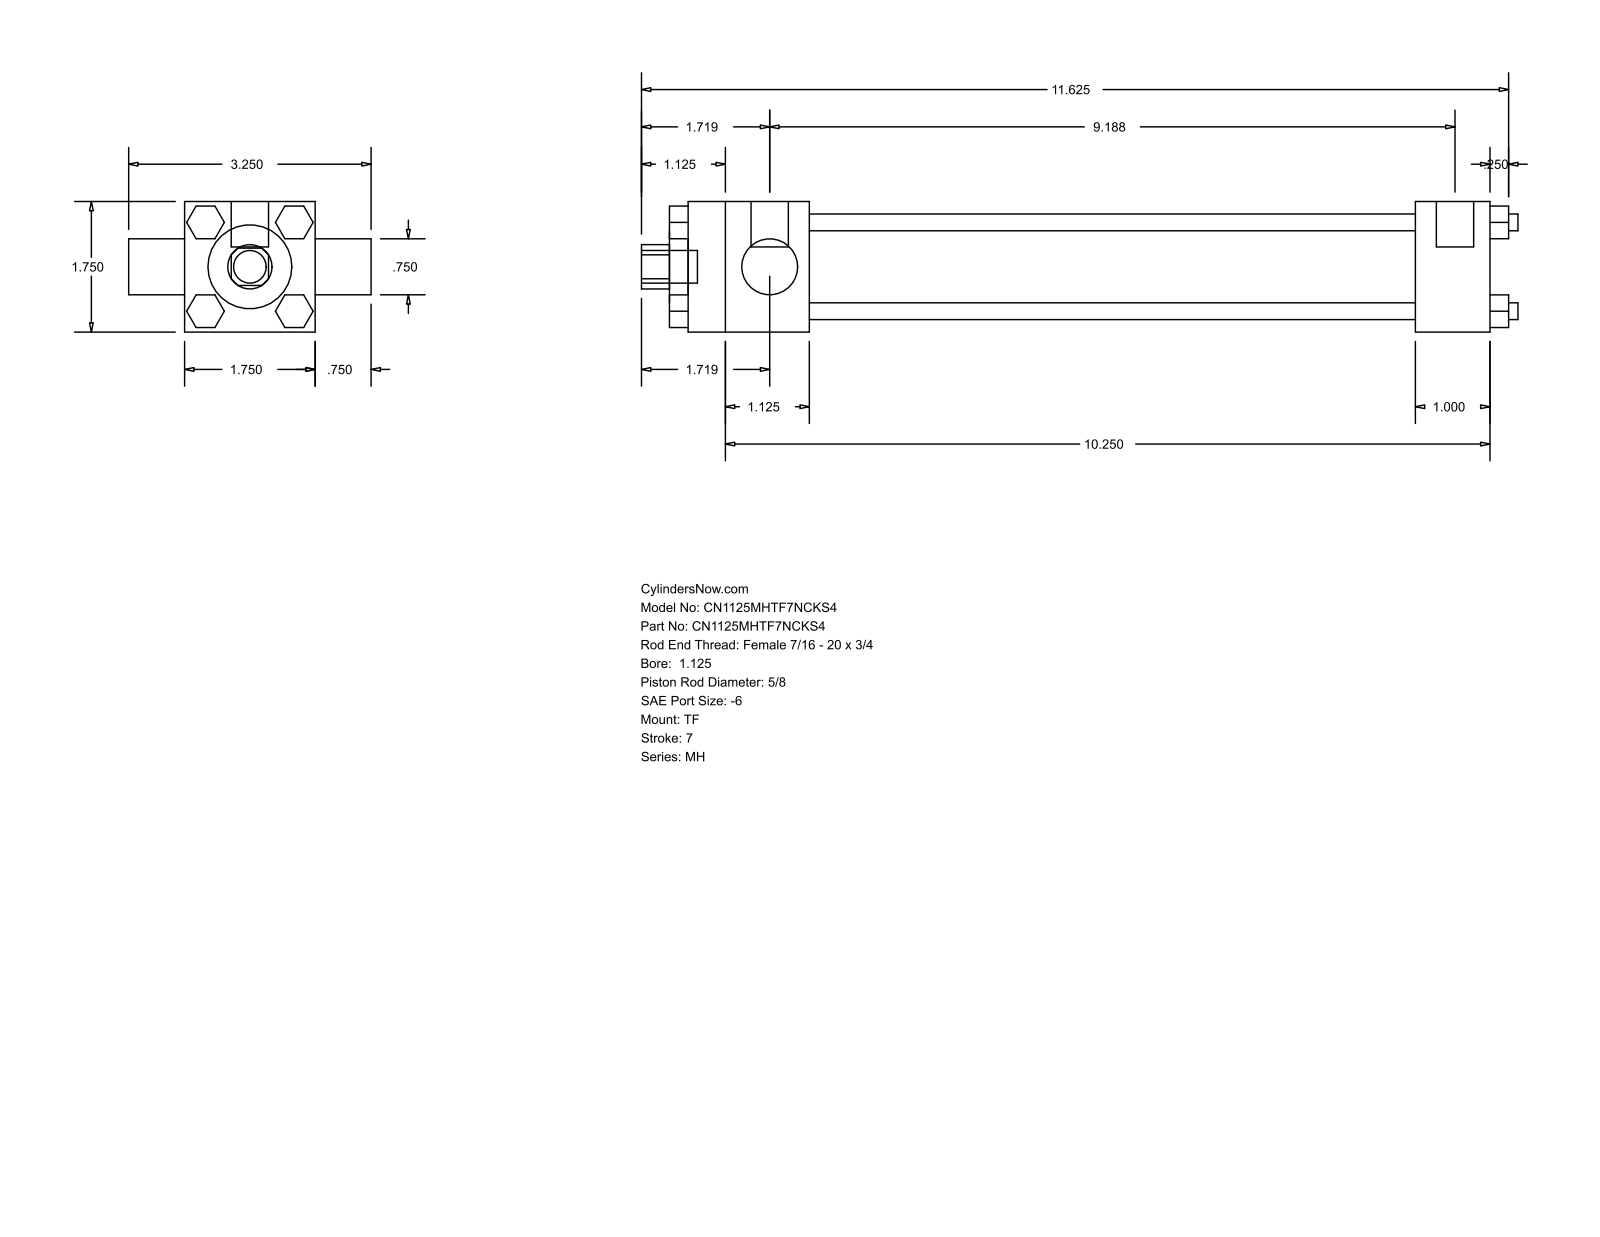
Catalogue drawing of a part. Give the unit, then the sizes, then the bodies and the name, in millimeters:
Units: millimetres
Overall size (bounding box): 298.45 × 82.55 × 44.45
Round holes (diameter × count): ⌀15.88 ×1, ⌀19.05 ×1, ⌀28.57 ×1, ⌀34.92 ×1
Round bosses / shafts (diameter × count): ⌀5.71 ×4, ⌀5.56 ×3, ⌀12.7 ×2, ⌀11.11 ×1
Partial cylindrical surfaces — rounded edges, fillets, slot ends (radius × count): R7.54 ×1
Main face-to-face distances: 44.46, 11.11, 206.37, 231.78, 25.41, 41.27, 247.64, 273.05, 47.62, 279.4
Bodies: 0 solids, 120 faces (92 planar, 28 cylindrical, 0 other)
Part name (STEP PRODUCT): MH_TF__0112_0.625
STEP written by: GSSL Pune (CONFIG_CONTROL_DESIGN)
